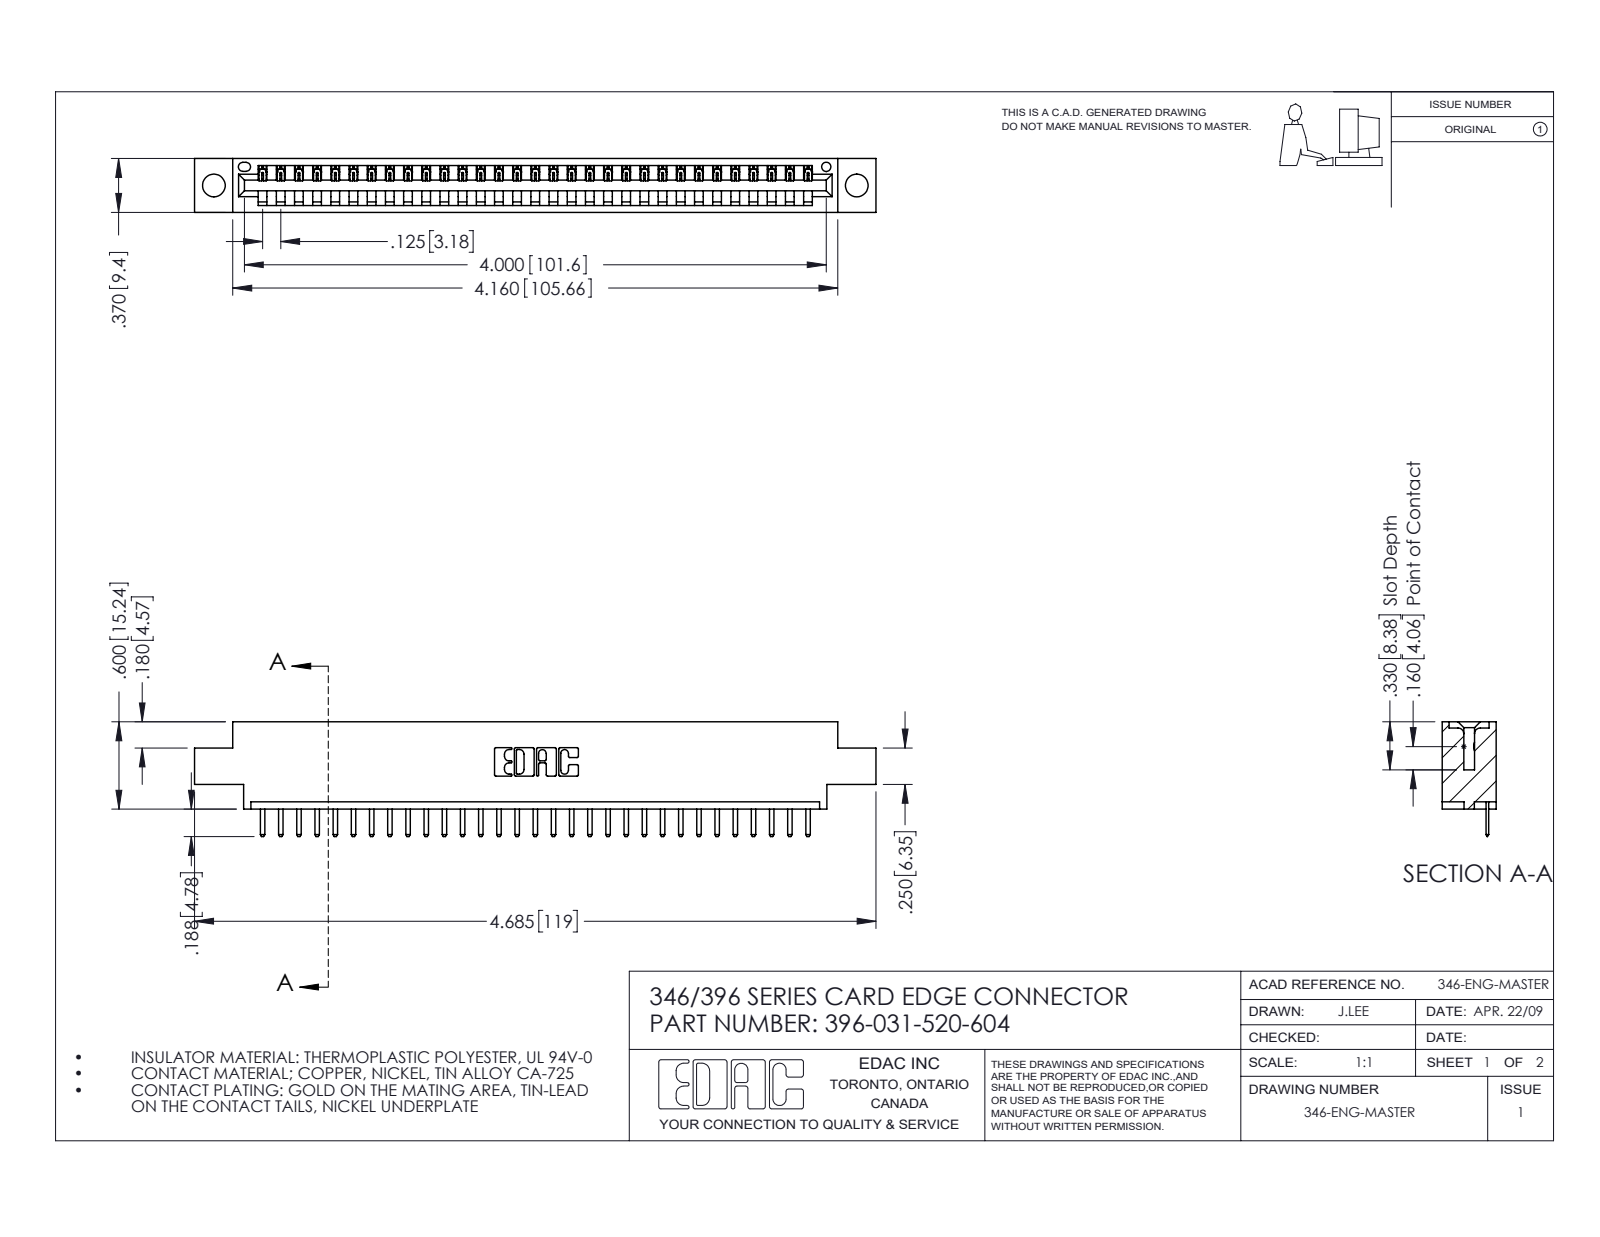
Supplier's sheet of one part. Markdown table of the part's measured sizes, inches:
| quantity | value |
| --- | --- |
| part name | 396-031-520-604; 346 Part_0.170 Offset - 0.156 Dia-TH; 345-292-001_345-293-120 |
| STEP written by | SolidWorks 2016 (CONFIG_CONTROL_DESIGN) |
| units | inches |
| bodies | 32 solids, 2048 faces (1382 planar, 666 cylindrical, 0 other) |
| overall size | 4.685 × 0.788 × 0.37 |
| volume | 0.67 in³ |
| surface area | 20.58 in² |
| round holes (diameter × count) | 0.156 × 2, 0.064 × 1 |
| partial cylindrical surfaces (radius × count) | 0.01 × 64, 0.006 × 62, 0.01 × 22, 0.007 × 6, 0.031 × 6, 0.026 × 3, 0.031 × 2, 0.04 × 2 |
| main face-to-face distances | 0.048, 0.322, 0.37, 0.25, 0.148, 0.222, 0.1, 0.174, 0.072, 0.298 |
| hole center spacings | 0.246, 4.212, 4.42 |
